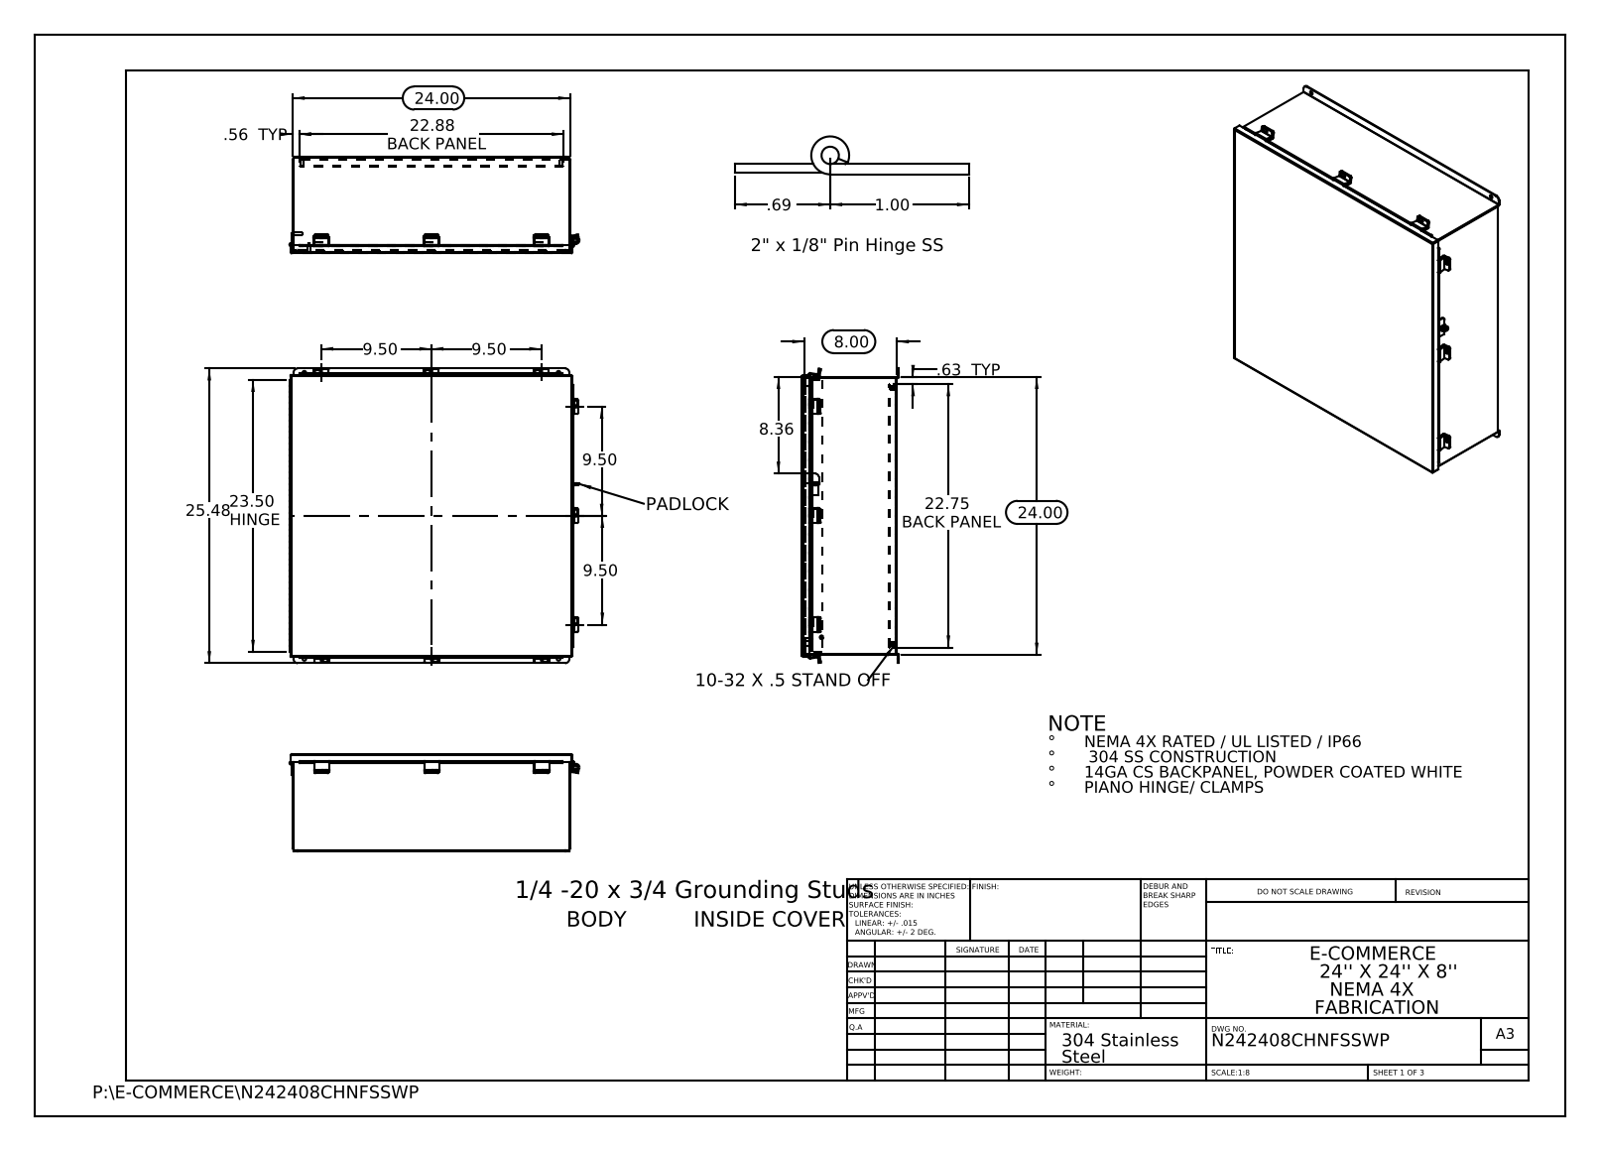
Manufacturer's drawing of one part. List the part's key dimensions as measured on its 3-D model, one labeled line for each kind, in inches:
Part name (STEP PRODUCT): N242408CHNFSSWP Hinge Body Side; N242408CHNFSSWP _JIC Hinge; N242408CHNFSSWP JIC Backpanel; N242408CHNFSSWP JIC Top (+8 more)
STEP written by: SolidWorks 2013 (CONFIG_CONTROL_DESIGN)
Units: inches
Bodies: 33 solids, 1148 faces (715 planar, 413 cylindrical, 20 other)
Overall size (bounding box): 25.476 × 25.072 × 8.39
Volume: 198.7 in³ · Surface area: 5 373 in²
Round holes (diameter × count): ⌀0.25 ×13, ⌀0.187 ×4, ⌀0.312 ×4, ⌀0.125 ×1, ⌀0.125 ×1, ⌀0.373 ×1, ⌀0.375 ×1
Round bosses / shafts (diameter × count): ⌀0.313 ×4, ⌀0.315 ×2, ⌀0.236 ×2, ⌀0.273 ×1, ⌀0.25 ×1
Partial cylindrical surfaces — rounded edges, fillets, slot ends (radius × count): R0.125 ×31, R0.133 ×18, R0.013 ×13, R0.009 ×12, R0.088 ×12, R0.083 ×6, R0.1 ×6, R0.375 ×4
Main face-to-face distances: 0.075, 8.128, 23.925, 8.053, 8.203, 7.628, 0.575, 0.5, 7.553, 0.649
Hole centre spacings: 1.315, 9.5, 22.213, 23.427, 32.257, 9.425, 19, 21.976
